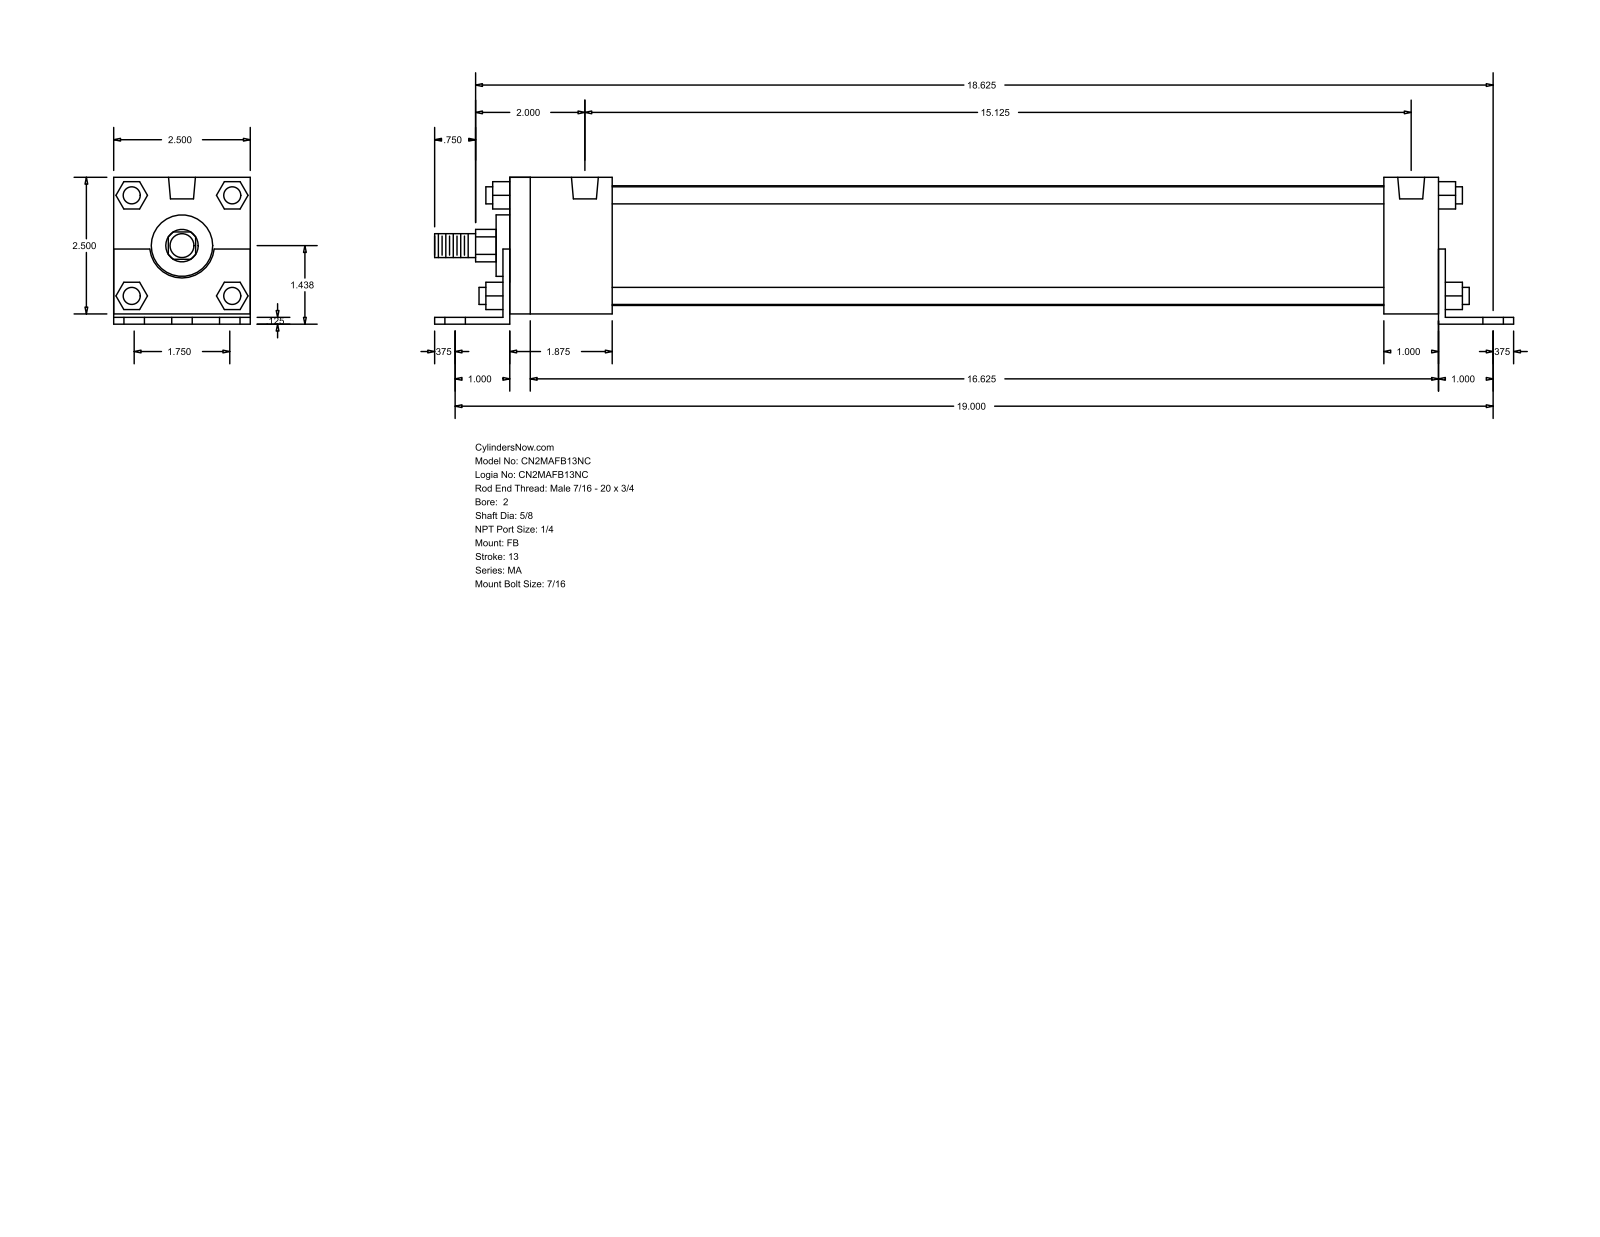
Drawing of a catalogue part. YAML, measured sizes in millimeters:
part_name: "MA_FB__0200_0.625"
step_written_by: "GSSL Pune (CONFIG_CONTROL_DESIGN)"
units: millimeters
bodies: {solids: 0, faces: 140, planar: 105, cylindrical: 35, other: 0}
overall_size: [501.65, 68.26, 63.5]
round_holes:
  - {diameter: 11.11, count: 6}
  - {diameter: 7.94, count: 4}
  - {diameter: 12.49, count: 2}
round_bosses_or_shafts:
  - {diameter: 7.94, count: 4}
  - {diameter: 55.63, count: 1}
  - {diameter: 28.57, count: 1}
  - {diameter: 15.88, count: 1}
  - {diameter: 11.11, count: 1}
partial_cylinders:
  - {radius: 7.54, count: 1}
  - {radius: 15.05, count: 1}
face_to_face_distances: [63.5, 3.17, 4.76, 68.26, 1.59, 65.09, 438.15, 3.18, 431.8, 434.97]
hole_center_spacings: [22.23, 483.11, 482.6, 44.1, 44.46, 64.3, 384.18, 422.85]
